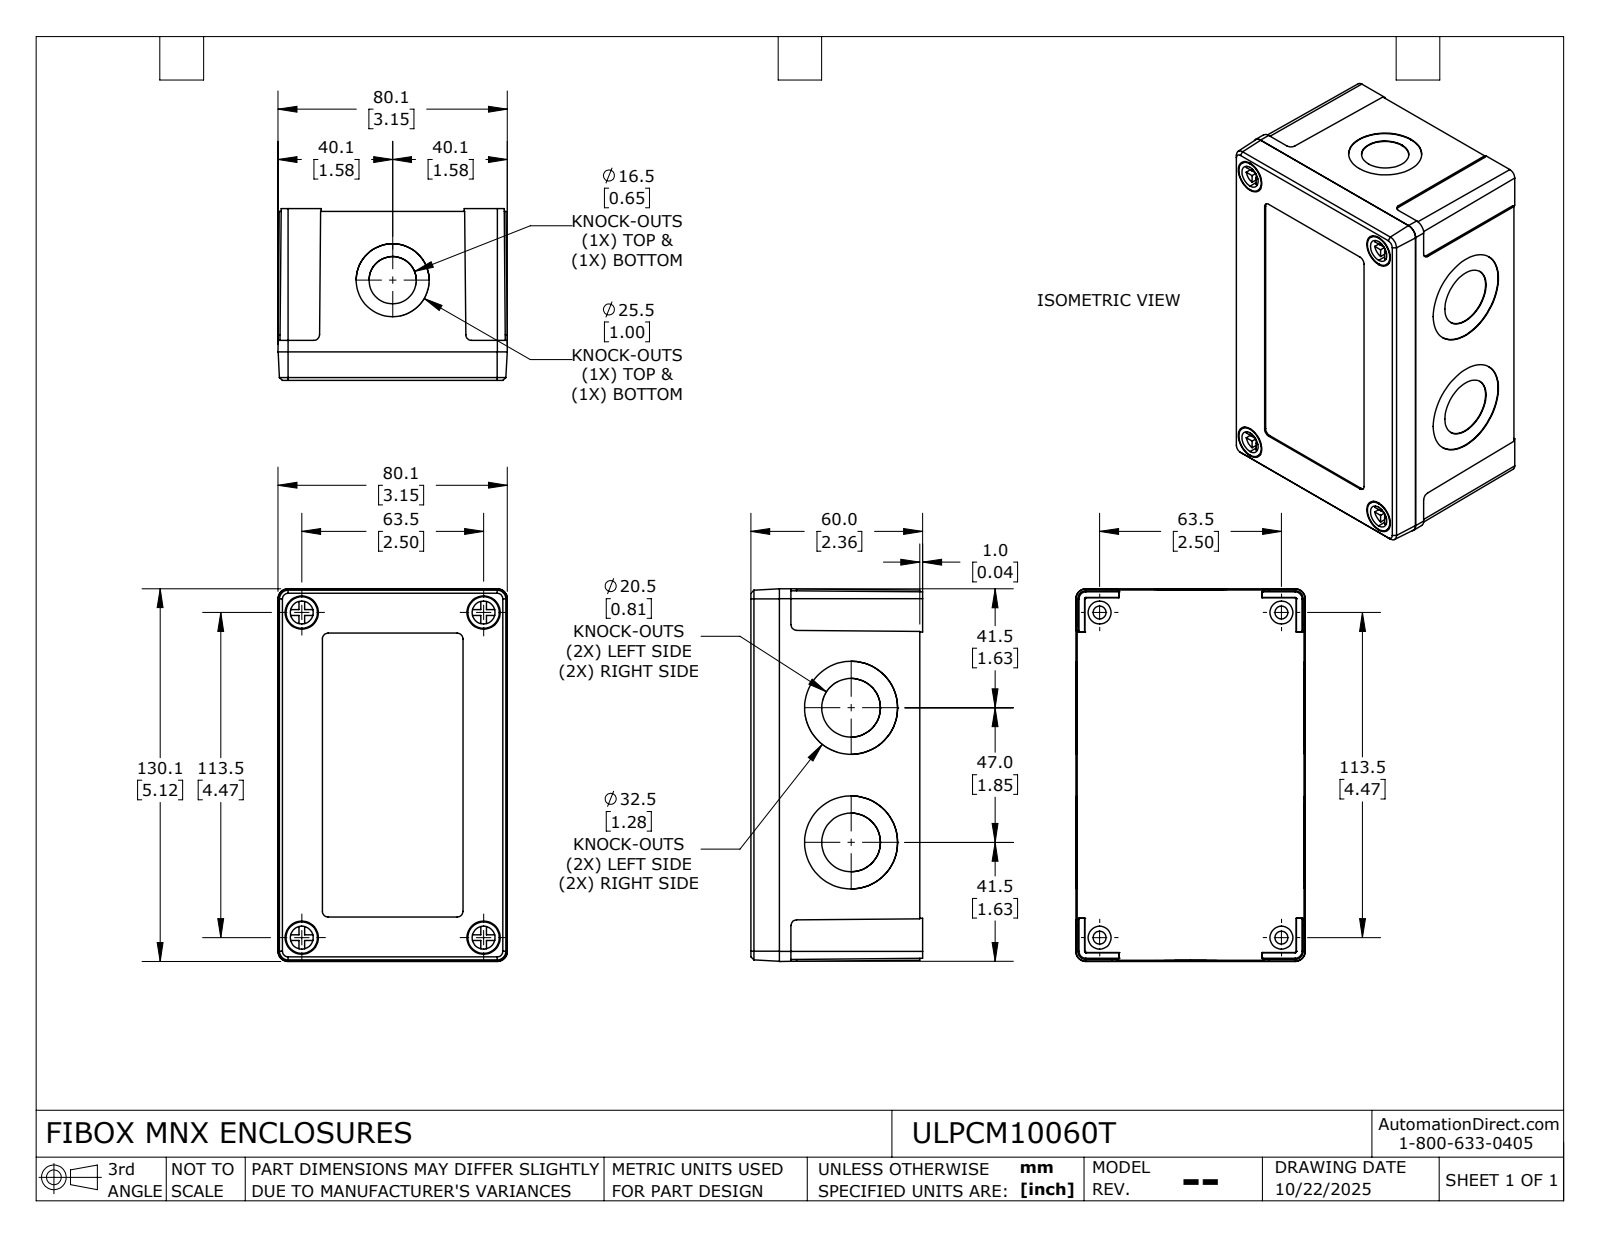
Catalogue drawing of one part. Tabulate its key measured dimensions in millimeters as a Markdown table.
| quantity | value |
| --- | --- |
| part name | ULPCM10060T_Default |
| STEP written by | SolidWorks 2024 (CONFIG_CONTROL_DESIGN) |
| units | millimeters |
| bodies | 6 solids, 510 faces (294 planar, 176 cylindrical, 40 other) |
| overall size | 130.1 × 80.1 × 60 |
| volume | 163 200 mm³ |
| surface area | 99 030 mm² |
| round holes (diameter × count) | 3.2 × 8, 4 × 8, 4.5 × 4, 8 × 4, 11.6 × 4, 20.5 × 4, 32.5 × 4, 16.5 × 2, 25.5 × 2 |
| round bosses / shafts (diameter × count) | 8 × 8, 2.5 × 8, 11 × 4, 7.2 × 4 |
| partial cylindrical surfaces (radius × count) | 2 × 8, 1.4 × 6, 0.5 × 4, 5 × 4, 0.6 × 2 |
| main face-to-face distances | 4.2, 56.7, 3, 53.7, 58.5, 55.5, 1.8, 56, 49, 59 |
| hole center spacings | 21.4, 22.6, 33.9, 37.5, 49.3, 54.8, 55.2, 57.9 |
